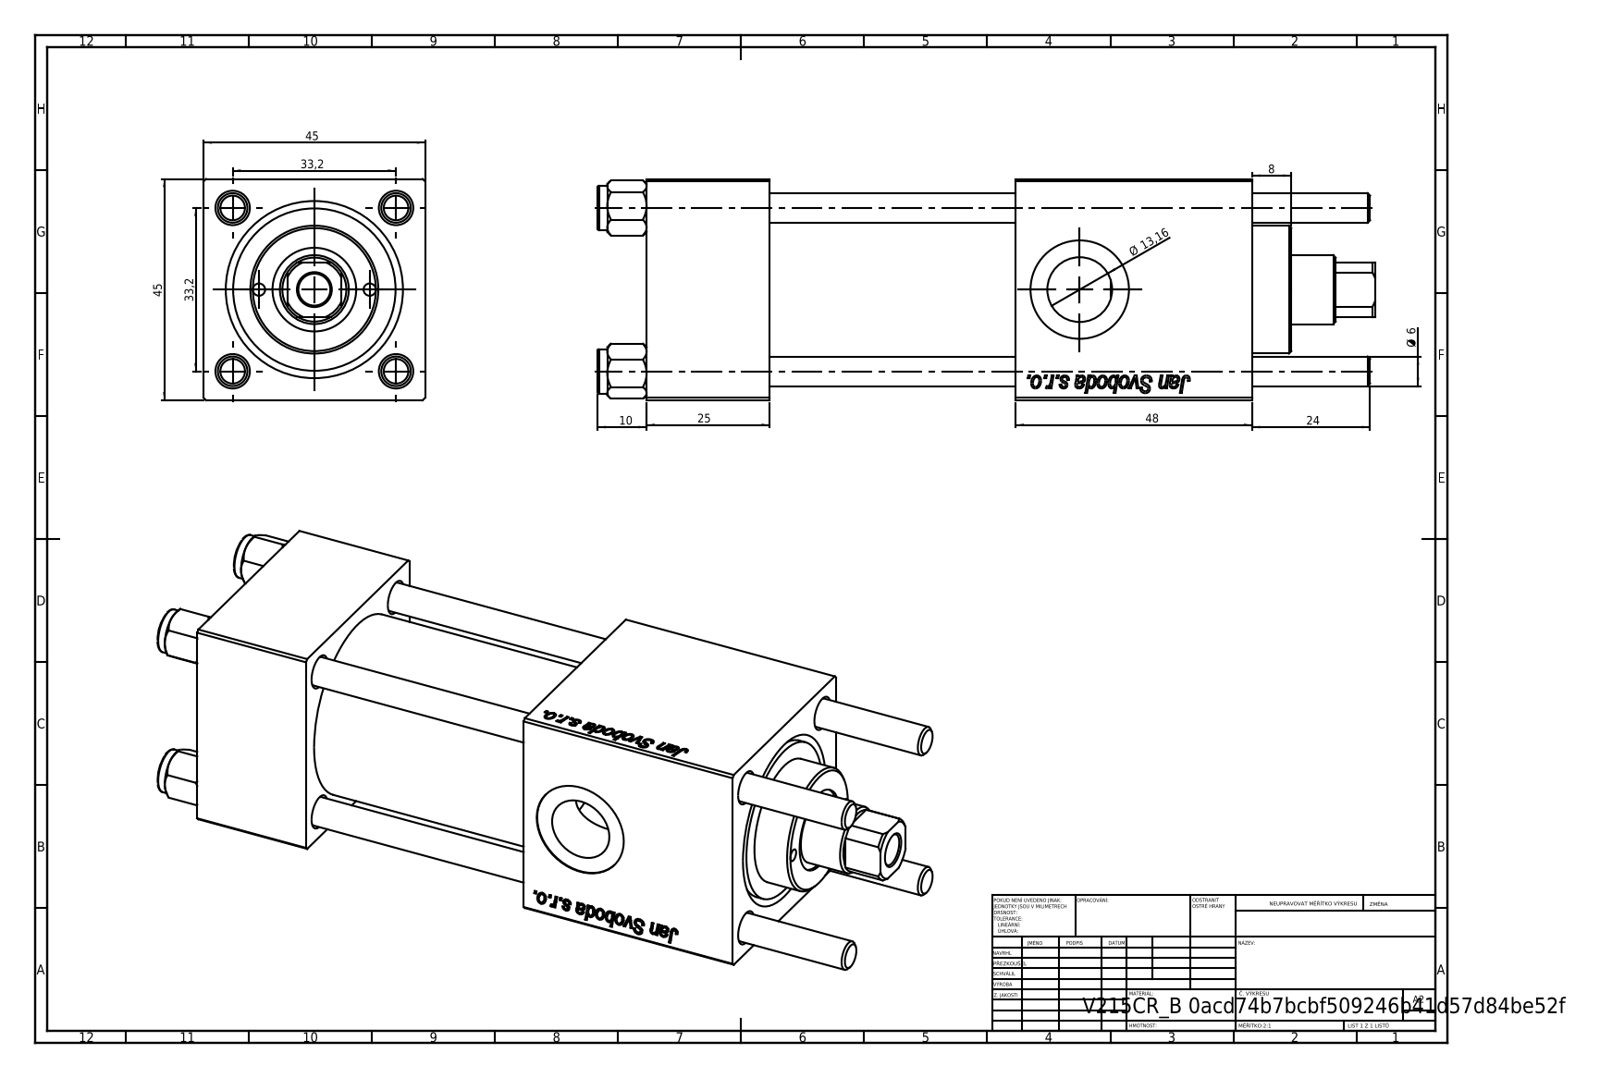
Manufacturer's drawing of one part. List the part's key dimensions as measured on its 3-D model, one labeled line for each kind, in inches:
Part name (STEP PRODUCT): V215CR_VCP_B; V215CR_B_TYCINKA; NUT_M5_B; V215_VC_A (+1 more)
STEP written by: SolidWorks 2019 (CONFIG_CONTROL_DESIGN)
Units: inches
Bodies: 11 solids, 1161 faces (431 planar, 82 cylindrical, 648 other)
Overall size (bounding box): 6.22 × 1.772 × 1.772
Volume: 12.11 in³ · Surface area: 112.7 in²
Round holes (diameter × count): ⌀0.236 ×4, ⌀0.098 ×2, ⌀0.276 ×2, ⌀0.518 ×2, ⌀0.787 ×2, ⌀0.256 ×1, ⌀0.551 ×1, ⌀0.669 ×1, ⌀0.945 ×1, ⌀1.26 ×1, ⌀1.299 ×1
Round bosses / shafts (diameter × count): ⌀0.354 ×4, ⌀1.496 ×1, ⌀1.024 ×1
Partial cylindrical surfaces — rounded edges, fillets, slot ends (radius × count): R0.256 ×1
Main face-to-face distances: 1.772, 0.984, 4.843, 3.858, 1.969, 2.953, 1.89, 3.713, 2.728, 0.76
Hole centre spacings: 0.687, 0.924, 1.276, 1.307, 0.443, 1.848, 0.886, 2.972
